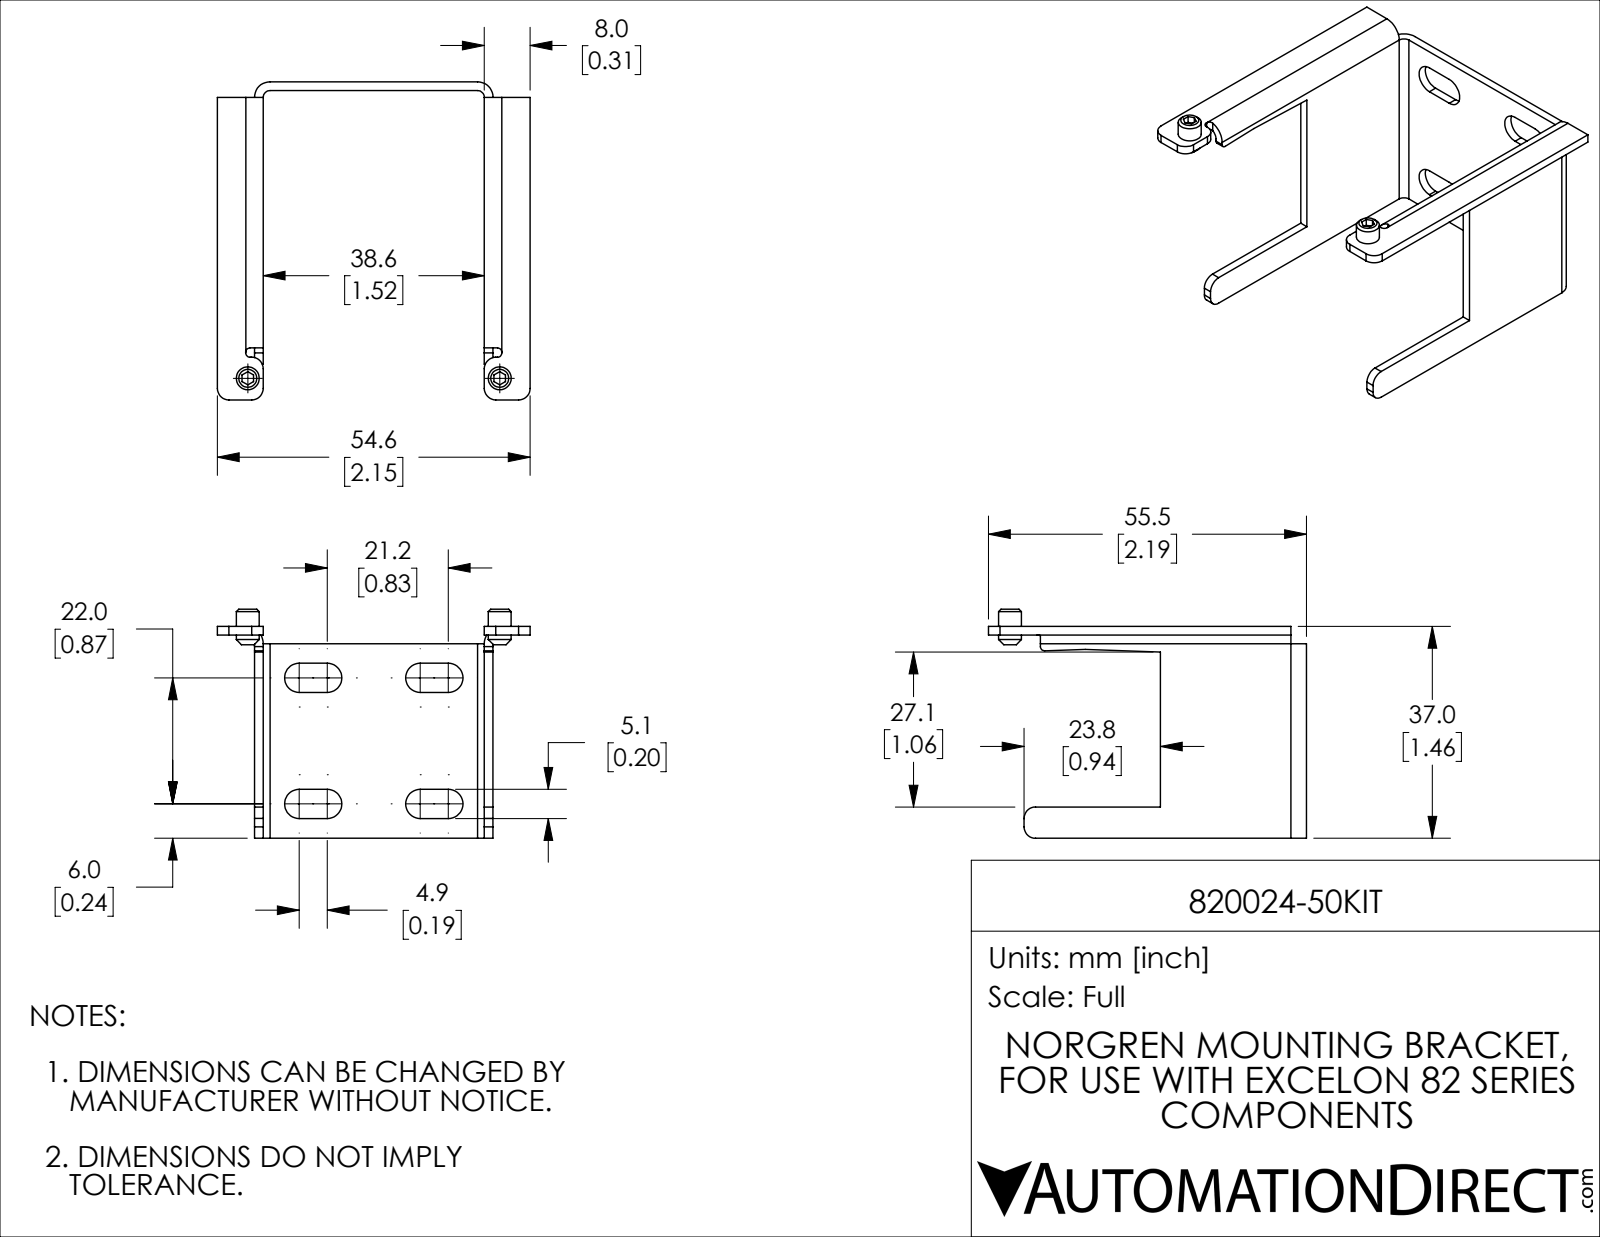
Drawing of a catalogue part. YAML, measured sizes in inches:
part_name: "820024-50KIT"
step_written_by: "SolidWorks 2021 (CONFIG_CONTROL_DESIGN)"
units: inches
bodies: {solids: 1, faces: 114, planar: 62, cylindrical: 44, other: 8}
overall_size: [2.186, 2.15, 1.574]
volume: 0.376
surface_area: 13.94
round_bosses_or_shafts:
  - {diameter: 0.157, count: 2}
partial_cylinders:
  - {radius: 0.079, count: 8}
  - {radius: 0.1, count: 8}
  - {radius: 0.03, count: 5}
  - {radius: 0.047, count: 2}
  - {radius: 0.06, count: 2}
  - {radius: 0.107, count: 2}
  - {radius: 0.12, count: 2}
face_to_face_distances: [0.06, 1.58, 1.52, 1.639, 1.396, 1.456, 0.255, 0.315, 1.835, 1.894]
